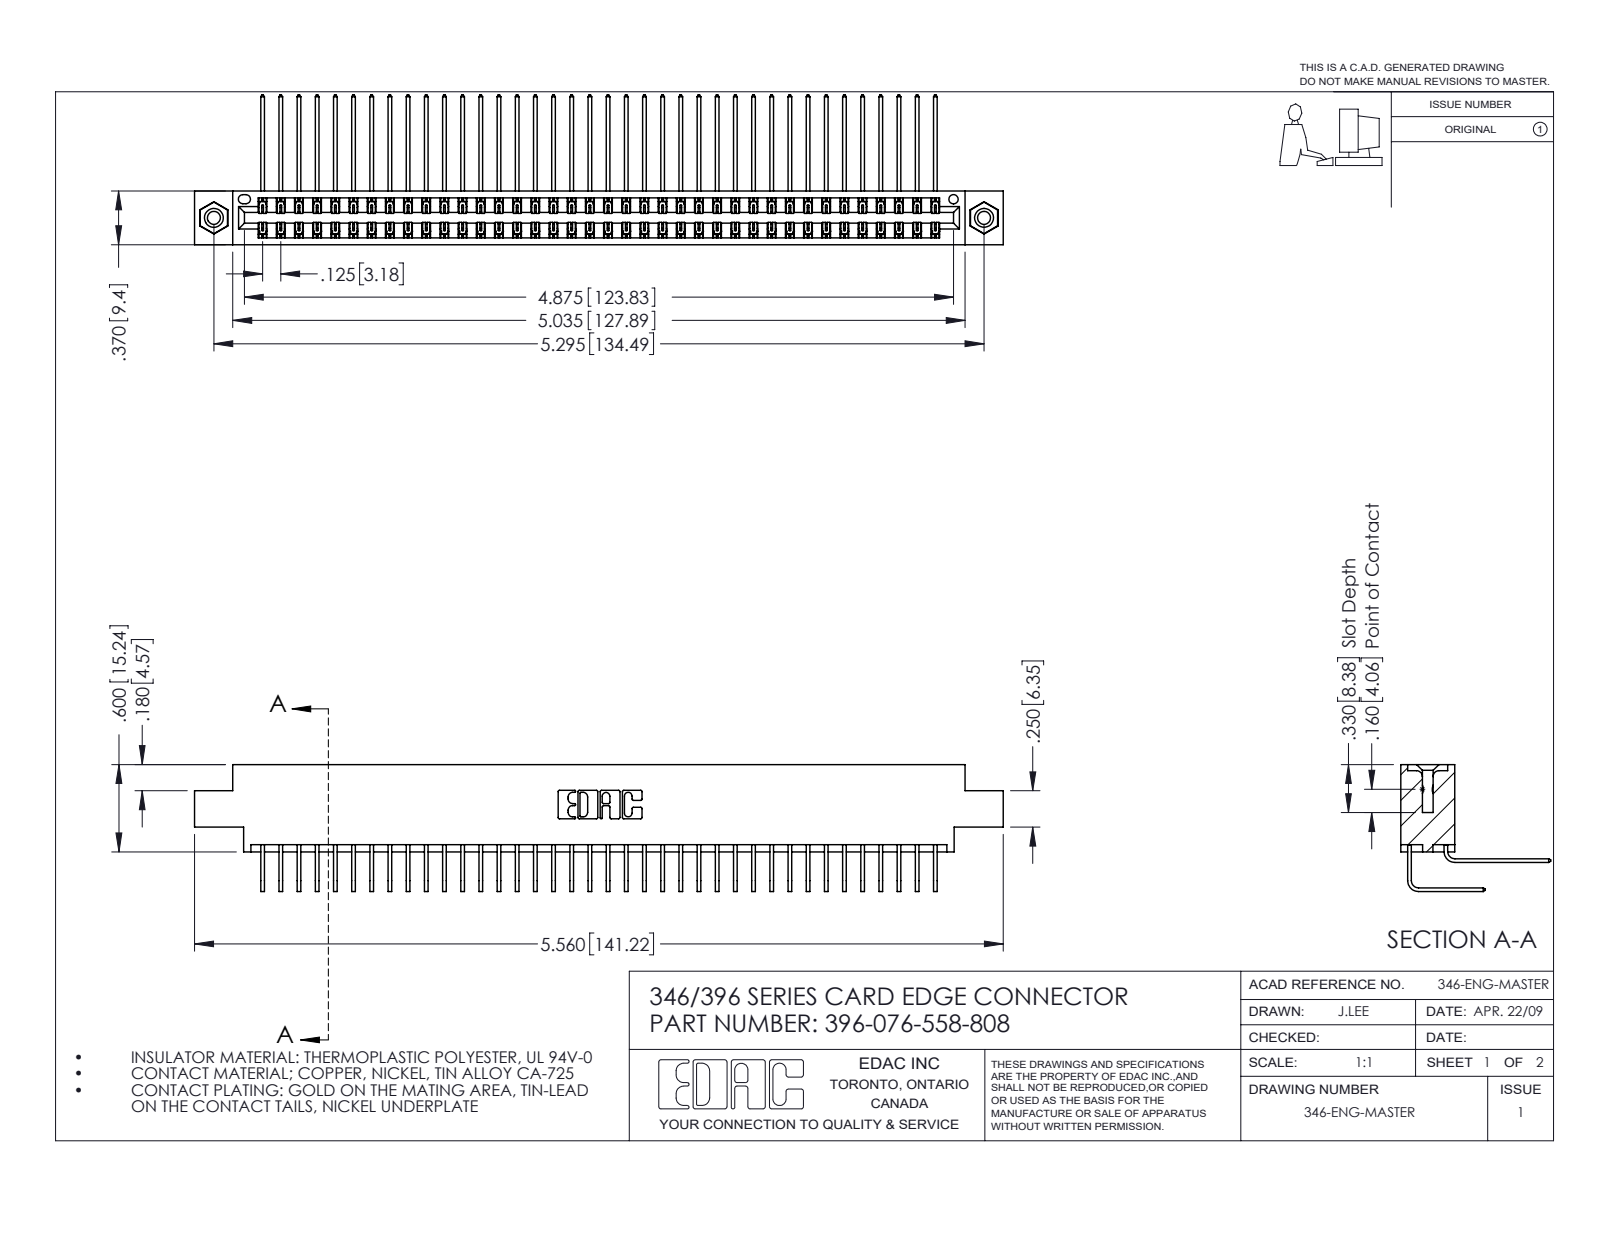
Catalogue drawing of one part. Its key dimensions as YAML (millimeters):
part_name: "345-292-001_558 Tail - 2; 345-292-001_558 559 Tail - 1; 346 Part_0.170 Offset - 0.156 Dia-TI; 345-250-001_345-250-003-102 (+1 more)"
step_written_by: "SolidWorks 2016 (CONFIG_CONTROL_DESIGN)"
units: millimeters
bodies: {solids: 79, faces: 4290, planar: 2924, cylindrical: 1350, other: 16}
overall_size: [141.2, 26.2, 22.2]
volume: 14000
surface_area: 21510
round_holes:
  - {diameter: 2.3, count: 2}
  - {diameter: 3.2, count: 2}
  - {diameter: 4, count: 2}
  - {diameter: 1.6, count: 1}
round_bosses_or_shafts:
  - {diameter: 3.9, count: 2}
partial_cylinders:
  - {radius: 0.2, count: 114}
  - {radius: 0.3, count: 22}
  - {radius: 0.2, count: 6}
  - {radius: 0.8, count: 6}
  - {radius: 0.7, count: 3}
  - {radius: 0.4, count: 2}
  - {radius: 0.6, count: 2}
  - {radius: 0.6, count: 2}
face_to_face_distances: [8.2, 1.2, 0.6, 9.4, 6.4, 7.6, 1.8, 7, 5.6, 3.8]
hole_center_spacings: [6.2, 129.2, 134.5]
